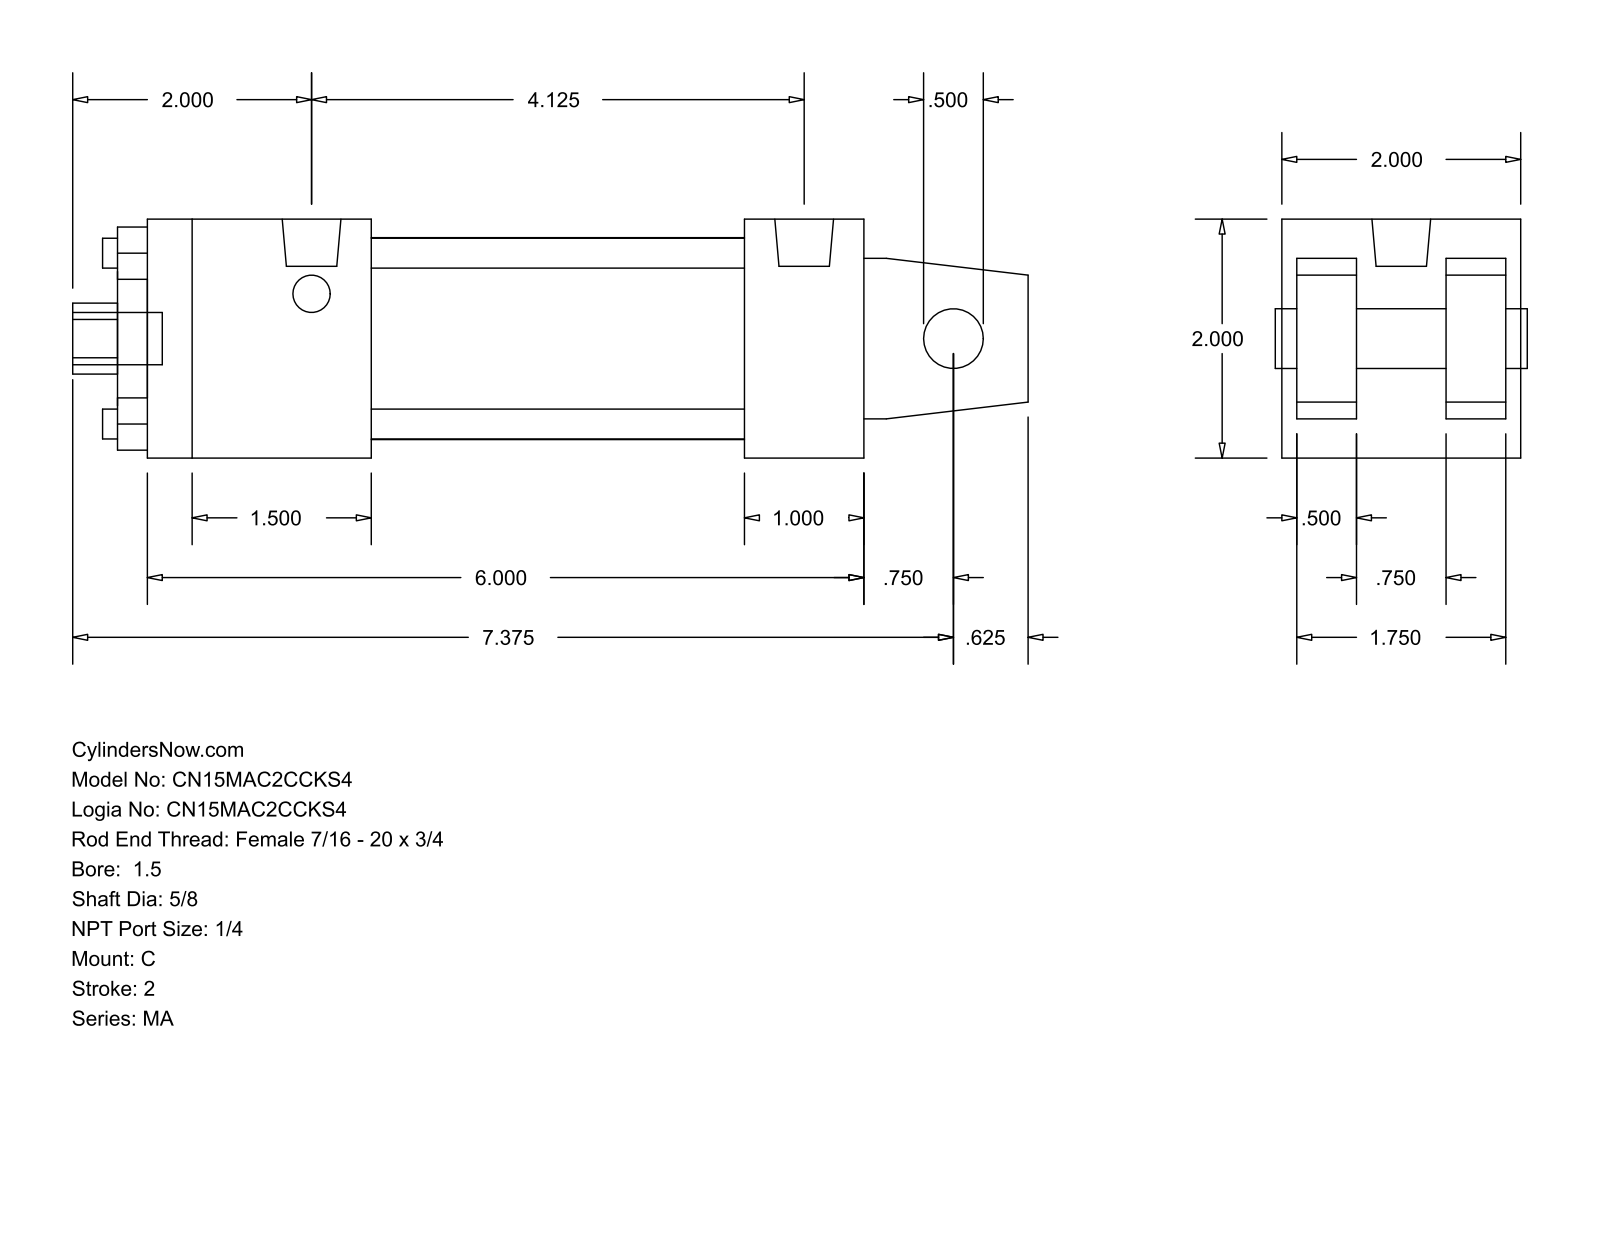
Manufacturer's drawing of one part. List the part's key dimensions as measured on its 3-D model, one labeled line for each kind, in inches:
Part name (STEP PRODUCT): MA_C__0150_0.625
STEP written by: GSSL Pune (CONFIG_CONTROL_DESIGN)
Units: inches
Bodies: 0 solids, 103 faces (76 planar, 27 cylindrical, 0 other)
Overall size (bounding box): 8 × 2 × 2
Round holes (diameter × count): ⌀0.25 ×4, ⌀0.5 ×1, ⌀0.625 ×1, ⌀1.125 ×1, ⌀1.69 ×1
Round bosses / shafts (diameter × count): ⌀0.313 ×4, ⌀0.492 ×2, ⌀0.437 ×1
Partial cylindrical surfaces — rounded edges, fillets, slot ends (radius × count): R0.297 ×1
Main face-to-face distances: 2, 0.5, 0.125, 0.625, 1.375, 1.875, 1.25, 6, 5, 1
Hole centre spacings: 1.011, 1.43, 2.022
